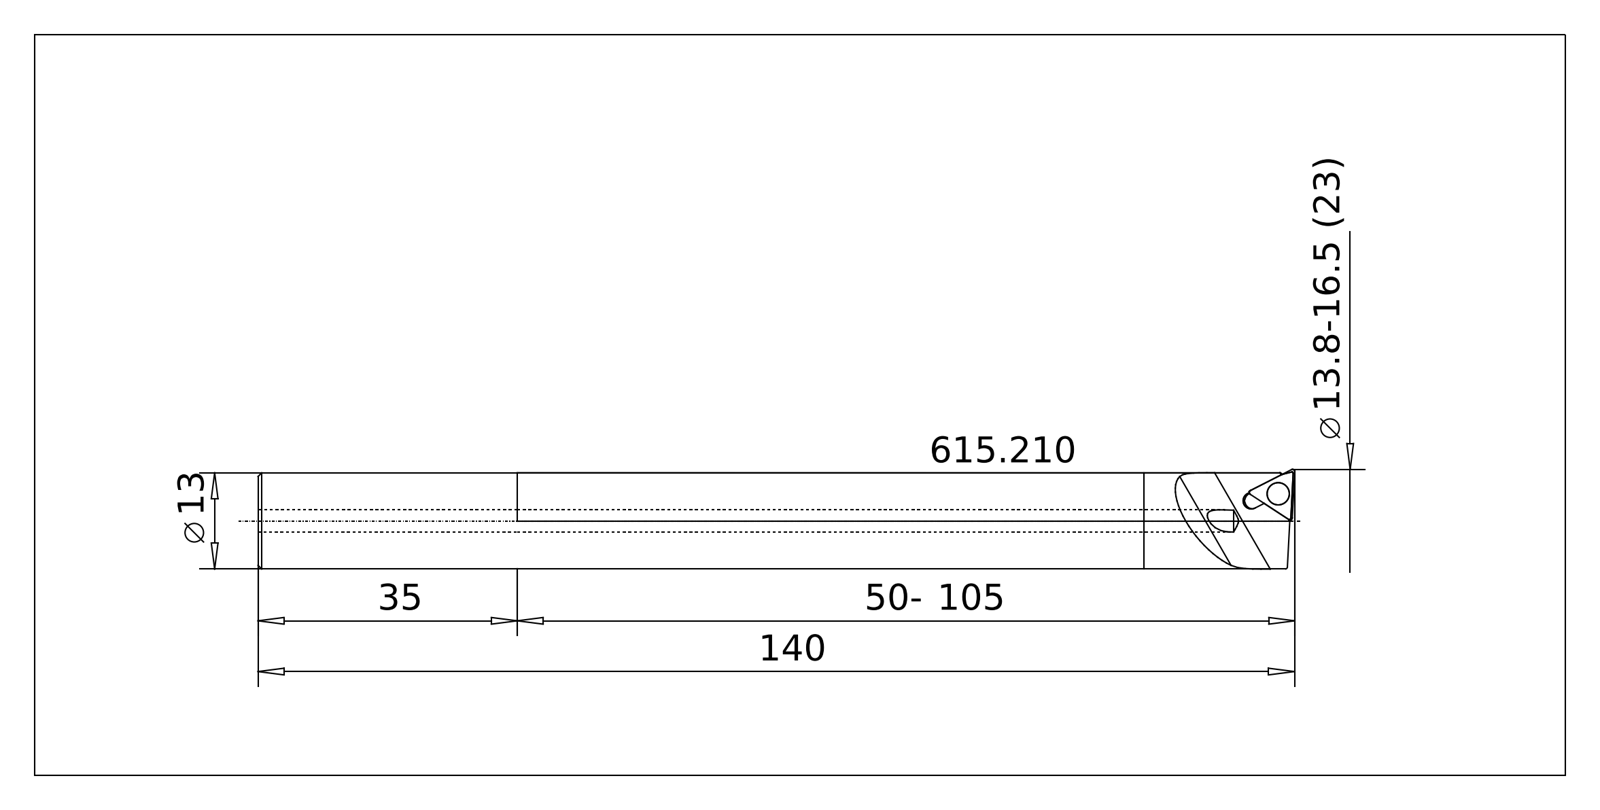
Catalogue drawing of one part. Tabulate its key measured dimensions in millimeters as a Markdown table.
| quantity | value |
| --- | --- |
| part name | 615.210 Kaiser E 14 TP07 X D13 X 140HM\|651.735 Kaiser TPGT 070203 K10C;Kombinieren1; 615.210 Kaiser E 14 TP07 X D13 X 140HM\|694.103 Kaiser ETL M2x4.8 T6 IP 10S;Kreismuster1; 615.210 Kaiser E 14 TP07 X D13 X 140HM\|615.210 Kaiser E 14 TP07 X D13 X 140HM;Verrundung2 |
| STEP written by | ACIS (automotive_design) |
| units | millimeters |
| bodies | 3 solids, 85 faces (19 planar, 35 cylindrical, 31 other) |
| overall size | 140.01 × 13.45 × 13 |
| volume | 16 790 mm³ |
| surface area | 7 161 mm² |
| round holes (diameter × count) | 1.56 × 1, 2 × 1, 2.3 × 1, 3 × 1 |
| round bosses / shafts (diameter × count) | 13 × 1, 2.7 × 1, 2 × 1 |
| partial cylindrical surfaces (radius × count) | 0.15 × 6, 0.3 × 6, 1.1 × 1, 5 × 1 |
| main face-to-face distances | 2.49, 2.37, 2.21, 1.6, 0.77, 0.89, 2.43, 4.03, 4.8, 4.92 |
